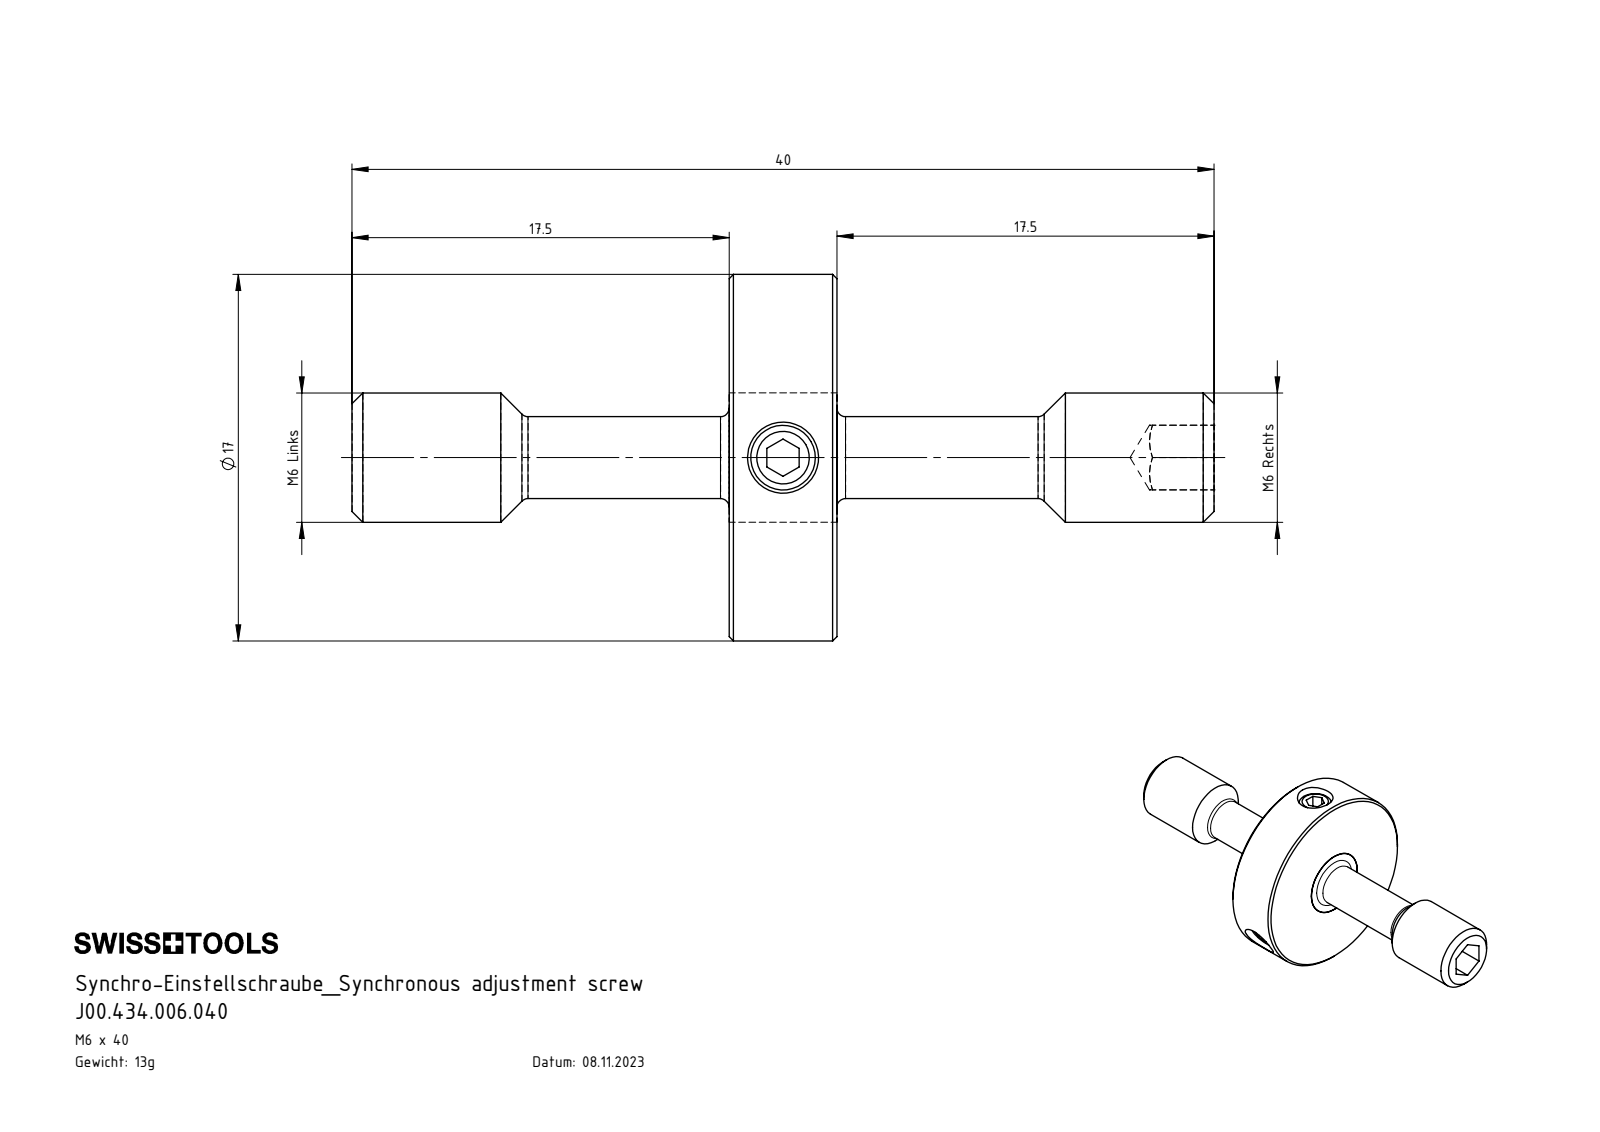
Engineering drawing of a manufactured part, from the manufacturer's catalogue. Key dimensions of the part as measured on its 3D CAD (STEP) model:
Part name (STEP PRODUCT): J00.434.006.040; Z42-ER3.001.040_A; Z42-ER3.002.005_A; ISO 4026 - M3 x 5
STEP written by: SolidWorks 2022 (AUTOMOTIVE_DESIGN)
Units: millimetres
Bodies: 5 solids, 99 faces (39 planar, 26 cylindrical, 34 other)
Overall size (bounding box): 40 × 17 × 17
Volume: 1 699 mm³ · Surface area: 1 807 mm²
Round holes (diameter × count): ⌀3.3 ×3
Round bosses / shafts (diameter × count): ⌀3 ×3, ⌀17 ×1, ⌀6 ×1, ⌀3.8 ×1
Main face-to-face distances: 5, 17.5, 22.5, 3, 1.5, 40, 19.25, 20.75, 1.75, 3.25
